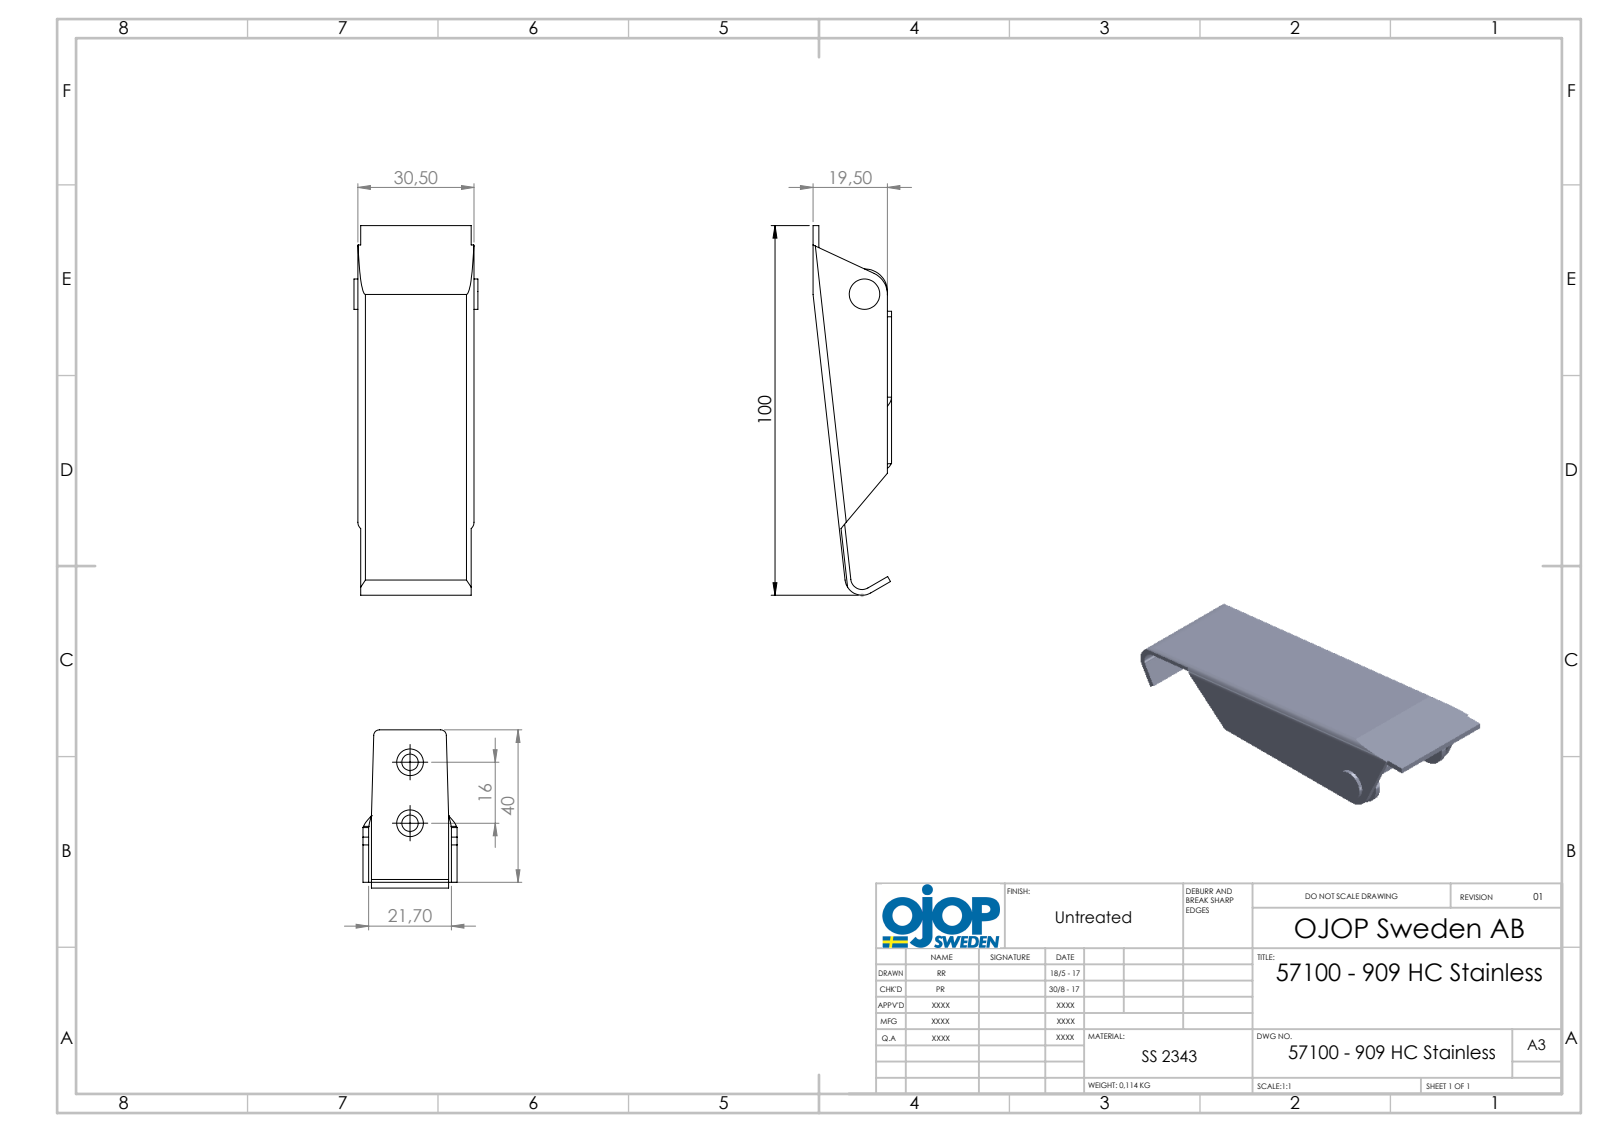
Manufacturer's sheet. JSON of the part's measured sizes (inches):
{"part_name": "nit; mellandel; underdel; överdel hake (+3 more)", "step_written_by": "SolidWorks 2015 (AUTOMOTIVE_DESIGN)", "units": "inches", "bodies": {"solids": 8, "faces": 175, "planar": 85, "cylindrical": 76, "other": 14}, "overall_size": [3.819, 1.28, 0.811], "volume_in3": 0.922, "surface_area_in2": 29.39, "round_holes": [[0.169, 2], [0.157, 1], [0.161, 1], [0.197, 1], [0.209, 1], [0.236, 1]], "round_bosses_or_shafts": [[0.394, 1], [0.315, 1], [0.276, 1], [0.236, 1], [0.154, 1]], "partial_cylinders_radius": [[0.079, 7], [0.039, 4], [0.029, 3], [0.088, 3], [0.059, 2], [0.118, 2], [0.236, 2], [0.02, 1]], "face_to_face_distances": [0.059, 1.142, 0.752, 1.083, 1.201, 0.098, 1.063, 1.043, 0.965, 0.079], "hole_center_spacings": [0.63, 1.561]}
